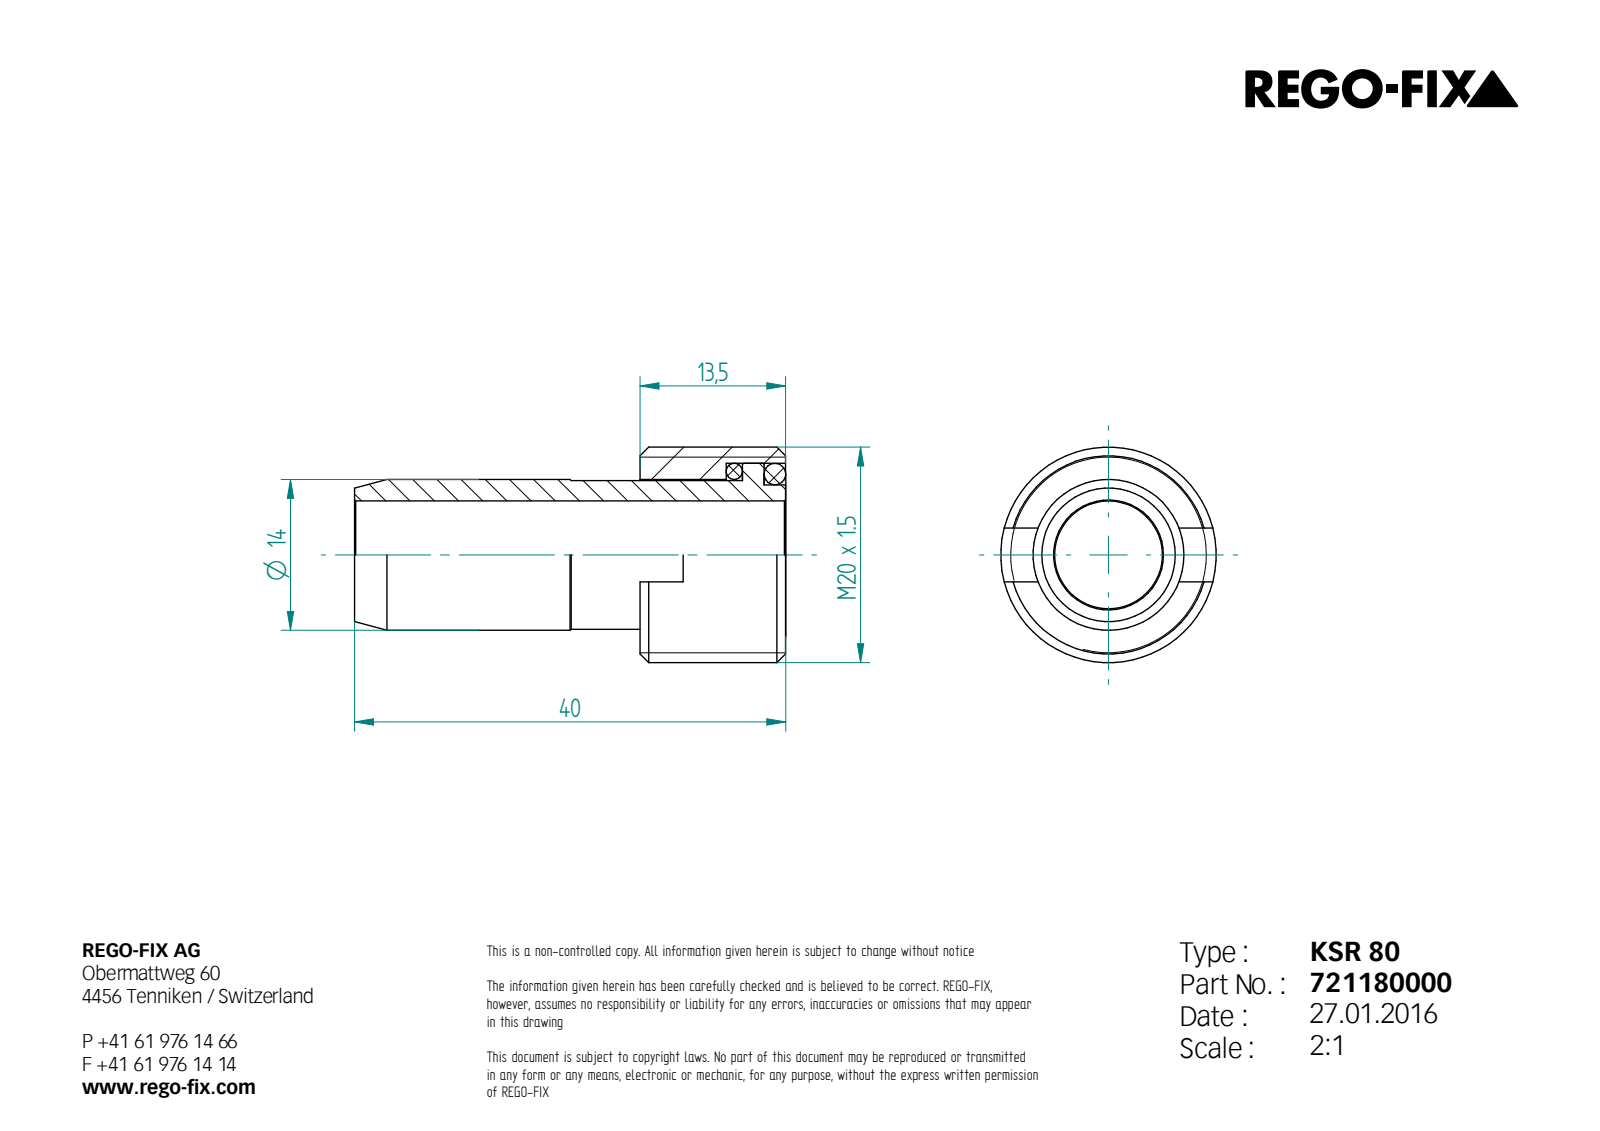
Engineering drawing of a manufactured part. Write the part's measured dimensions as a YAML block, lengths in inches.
part_name: "0012568; 0012569; 0012570; 0012571"
step_written_by: "Unknown (AUTOMOTIVE_DESIGN)"
units: inches
bodies: {solids: 4, faces: 33, planar: 14, cylindrical: 8, other: 11}
overall_size: [1.575, 0.787, 0.787]
volume: 0.295
surface_area: 8.567
round_holes:
  - {diameter: 0.394, count: 1}
  - {diameter: 0.551, count: 1}
  - {diameter: 0.669, count: 1}
round_bosses_or_shafts:
  - {diameter: 0.787, count: 1}
  - {diameter: 0.543, count: 1}
  - {diameter: 0.512, count: 1}
face_to_face_distances: [0.079, 0.157, 0.217, 0.374, 0.531, 0.453, 0.315, 0.138, 0.059, 1.043]
